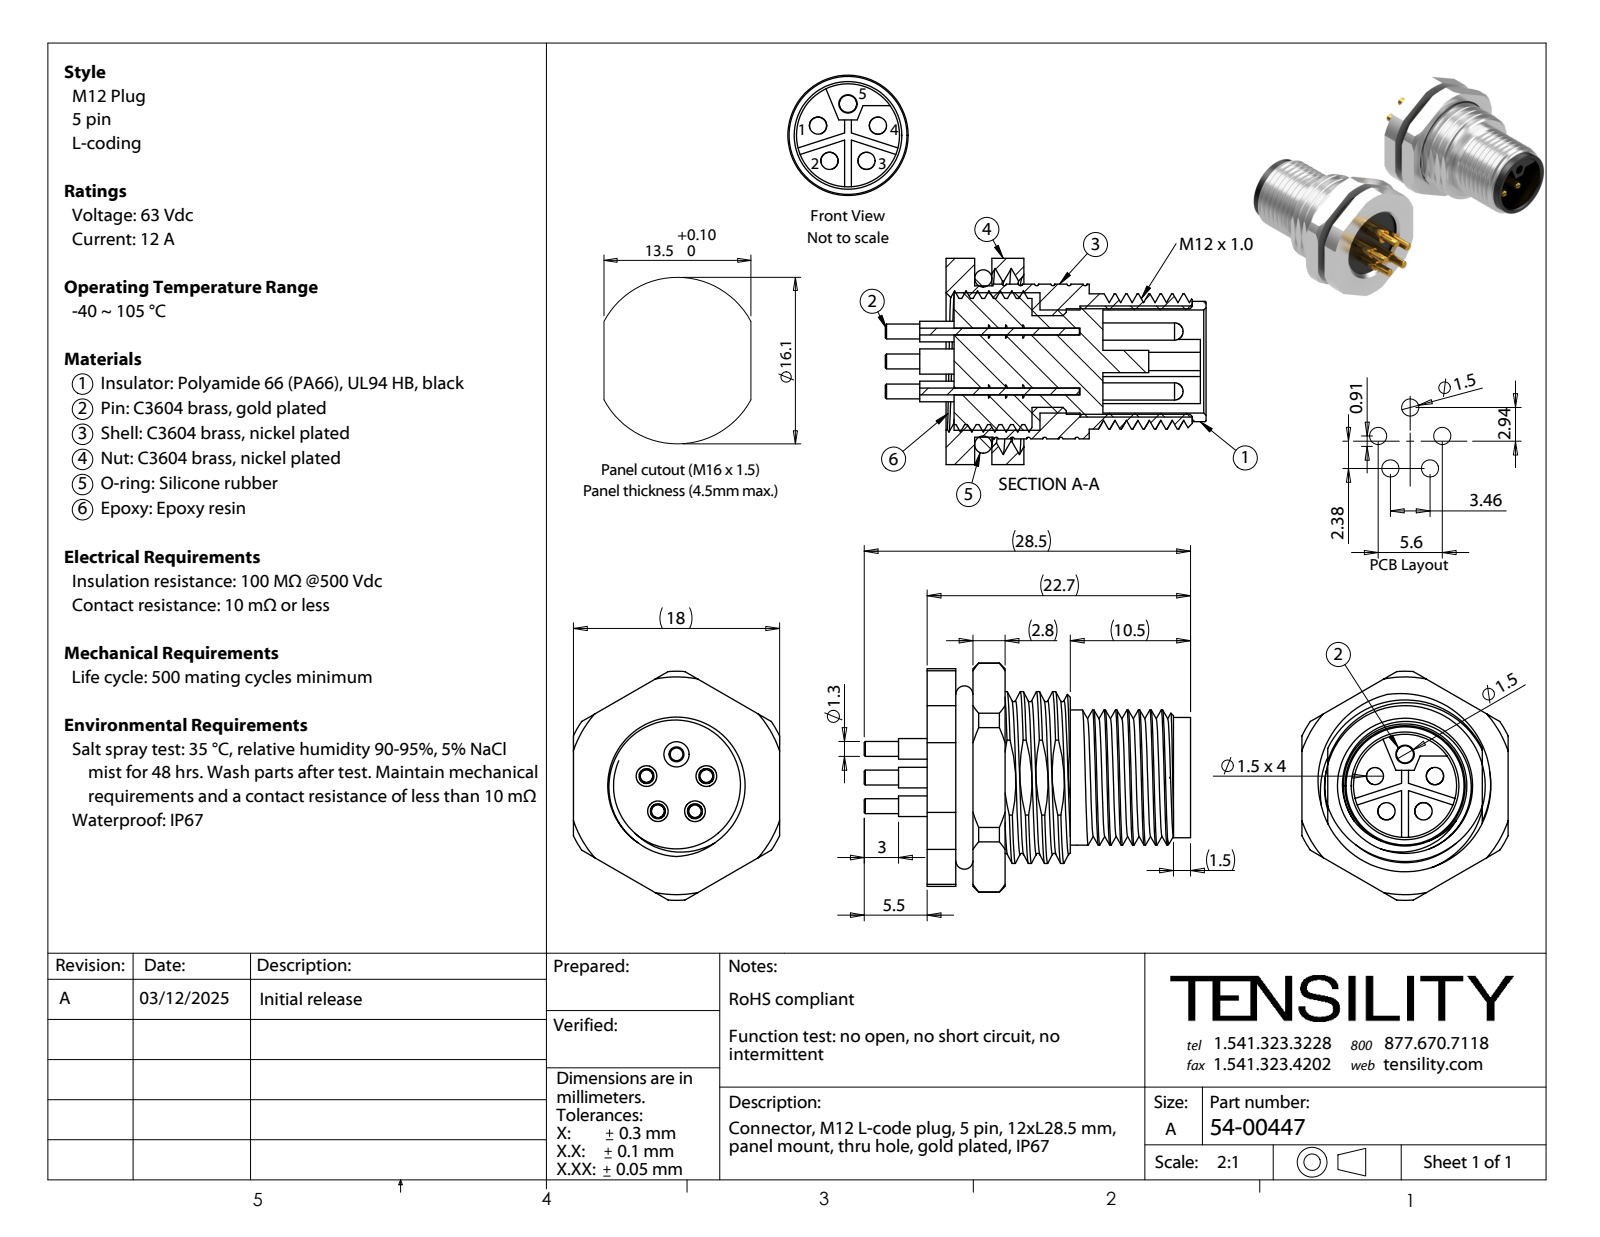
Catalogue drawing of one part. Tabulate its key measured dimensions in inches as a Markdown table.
| quantity | value |
| --- | --- |
| part name | 54-00447-06; 54-00447-03; 54-00447-05; 54-00447-01 (+3 more) |
| STEP written by | SolidWorks 2021 (CONFIG_CONTROL_DESIGN) |
| units | inches |
| bodies | 9 solids, 360 faces (102 planar, 152 cylindrical, 106 other) |
| overall size | 1.102 × 0.783 × 0.757 |
| volume | 0.202 in³ |
| surface area | 9.34 in² |
| round holes (diameter × count) | 0.059 × 5, 0.063 × 1, 0.315 × 1, 0.354 × 1, 0.362 × 1, 0.433 × 1, 0.551 × 1 |
| round bosses / shafts (diameter × count) | 0.051 × 5, 0.071 × 4, 0.52 × 1, 0.472 × 1, 0.465 × 1, 0.413 × 1, 0.382 × 1, 0.087 × 1 |
| partial cylindrical surfaces (radius × count) | 0.295 × 1, 0.374 × 1, 0.394 × 1 |
| main face-to-face distances | 0.028, 0.268, 0.098, 0.169, 0.709, 0.197, 0.295, 0.071, 0.157, 0.059 |
| hole center spacings | 0.108, 0.206, 0.128, 0.127, 0.206 |
